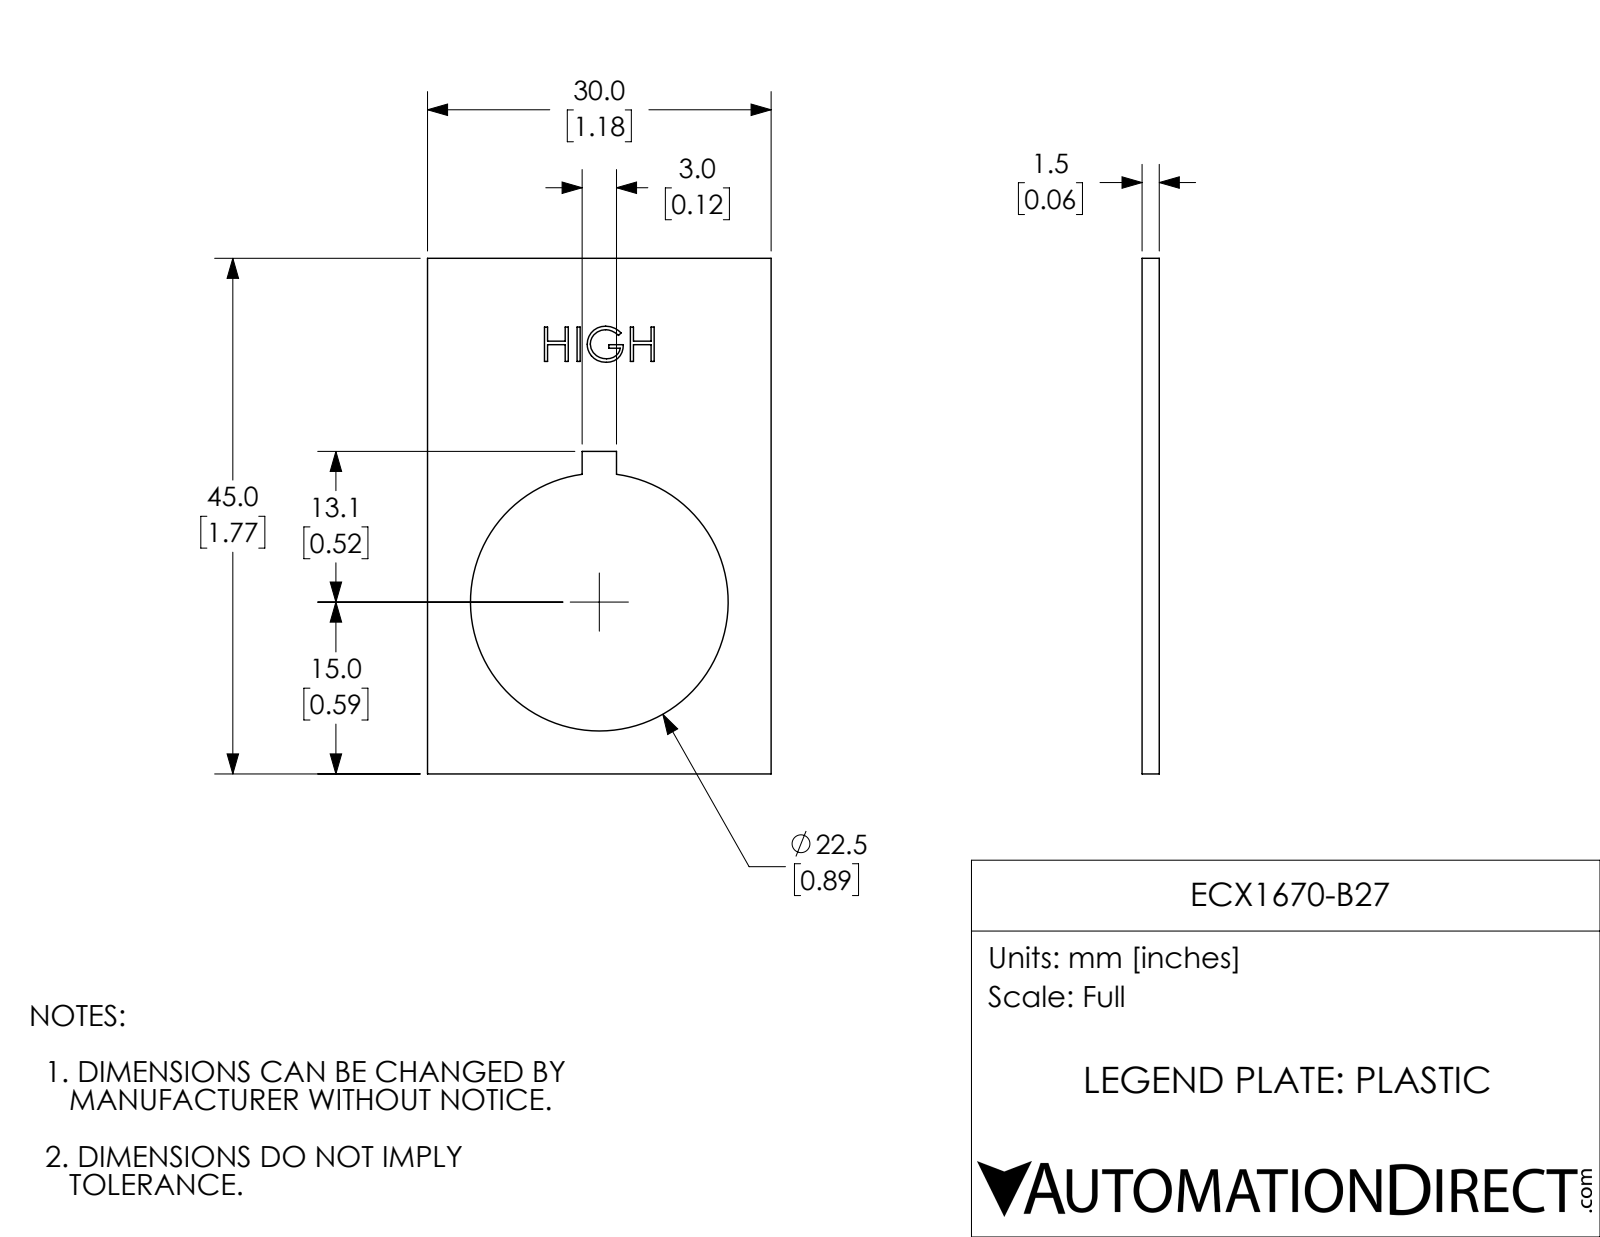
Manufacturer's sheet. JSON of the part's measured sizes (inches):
{"part_name": "ECX1670-B27", "step_written_by": "SolidWorks 2017 (AUTOMOTIVE_DESIGN)", "units": "inches", "bodies": {"solids": 1, "faces": 57, "planar": 45, "cylindrical": 3, "other": 9}, "overall_size": [1.772, 1.181, 0.059], "volume_in3": 0.087, "surface_area_in2": 3.459, "round_holes": [[0.886, 1]], "face_to_face_distances": [0.059, 1.181, 1.772, 0.058, 0.531, 0.65, 1.108, 0.663, 0.118, 0.295]}
